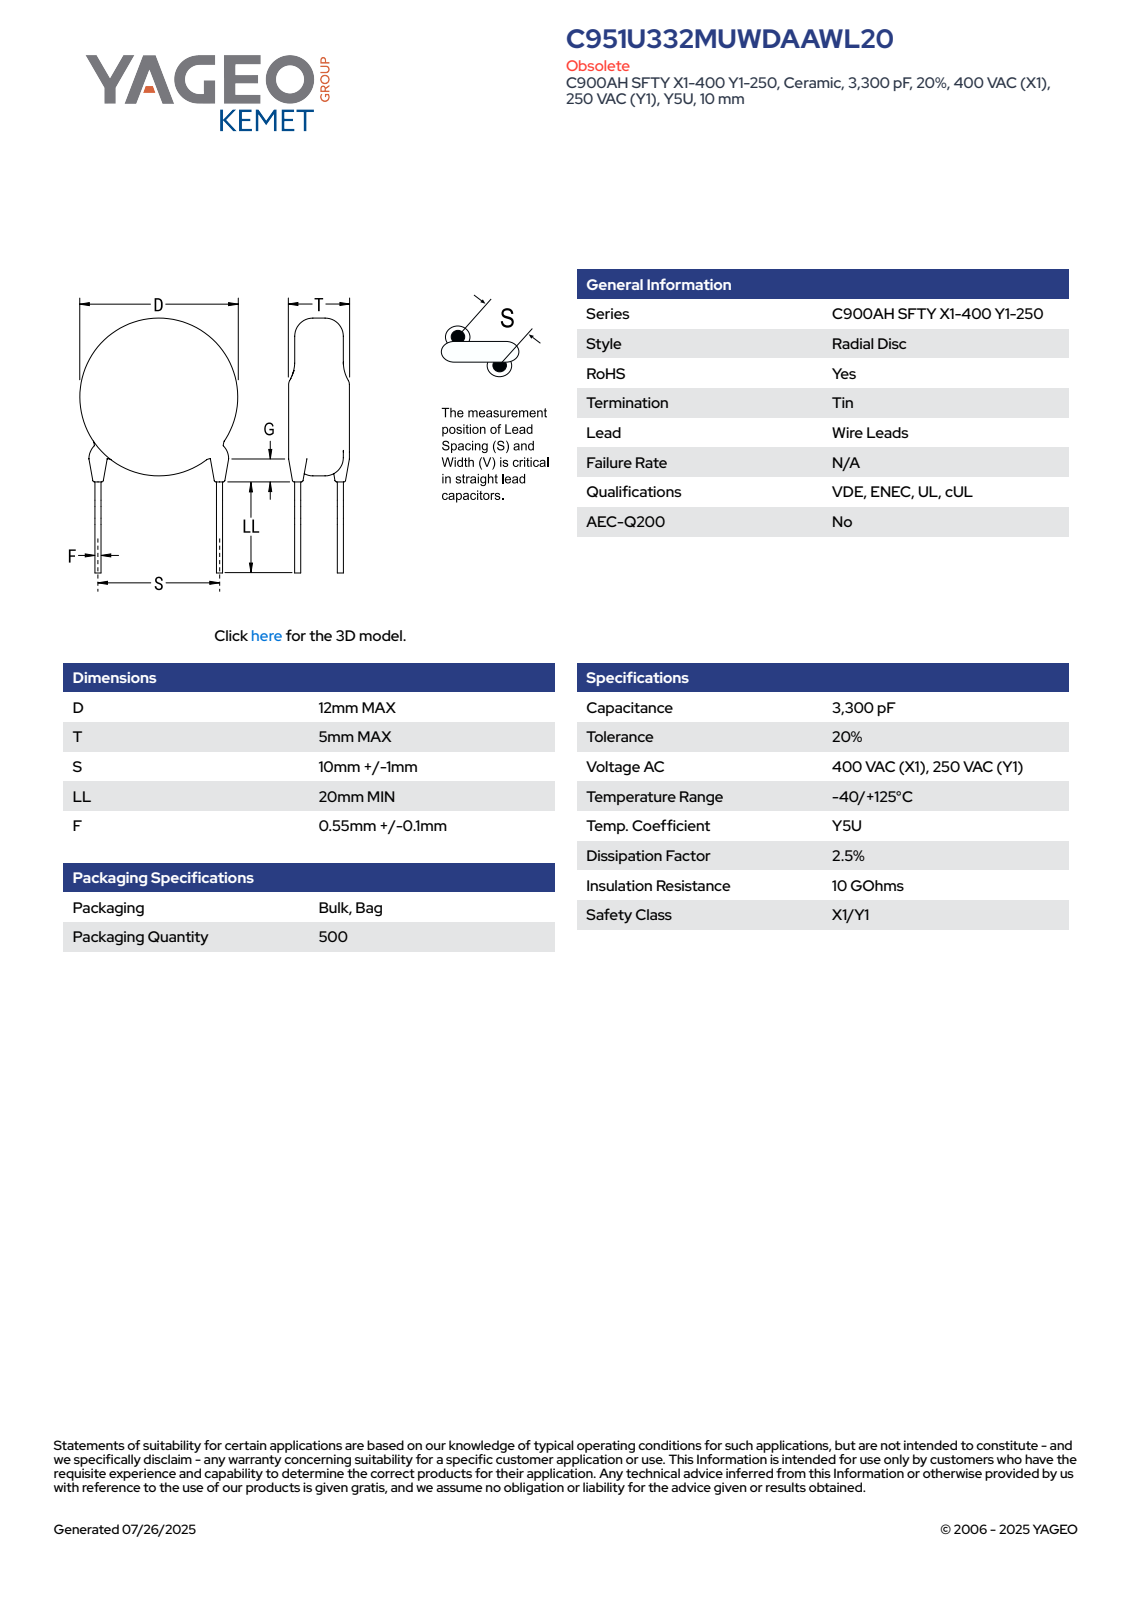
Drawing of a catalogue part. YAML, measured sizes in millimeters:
part_name: "CCD_STC900_D12T5S10LL20F0.65G3"
step_written_by: "SolidWorks 2014 (AUTOMOTIVE_DESIGN)"
units: millimeters
bodies: {solids: 4, faces: 83, planar: 61, cylindrical: 6, other: 16}
overall_size: [32.33, 12, 5]
volume: 567
surface_area: 486
round_bosses_or_shafts:
  - {diameter: 0.65, count: 2}
  - {diameter: 12, count: 1}
face_to_face_distances: [5, 27.02, 25.64, 1.38, 0.38, 0.34, 0.6, 5.66, 1.12, 0.86]
